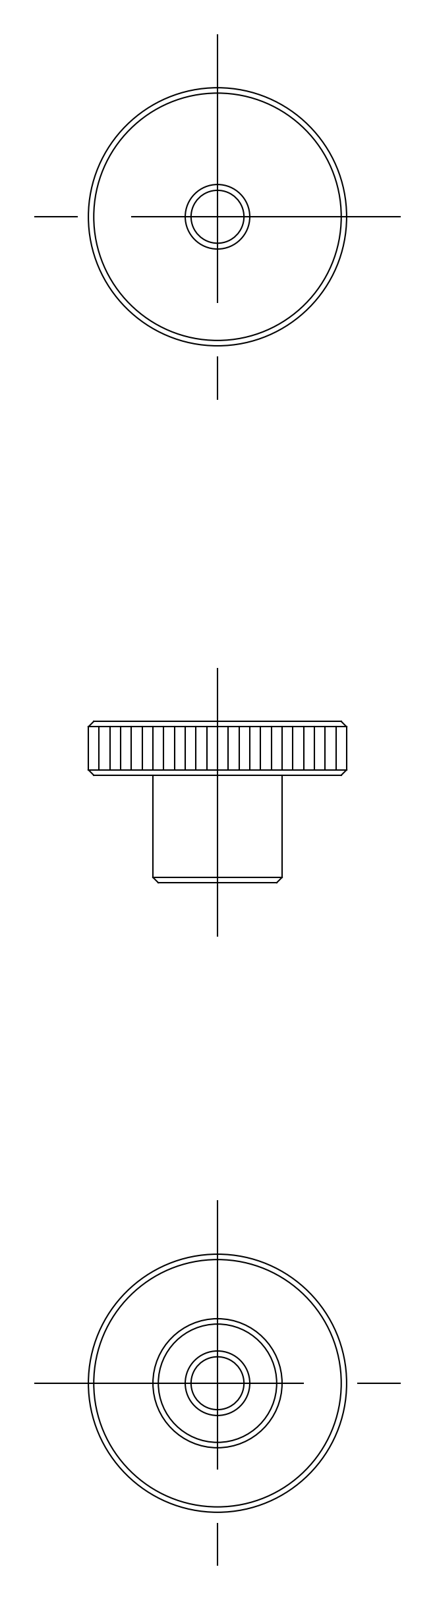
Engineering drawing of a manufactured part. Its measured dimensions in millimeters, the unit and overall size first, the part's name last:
Units: millimetres
Overall size (bounding box): 24 × 24 × 15
Volume: 2 950 mm³ · Surface area: 1 830 mm²
Bodies: 1 solid, 15 faces (0 planar, 0 cylindrical, 15 other)
Part name (STEP PRODUCT): knob
STEP written by: CADfix (AUTOMOTIVE_DESIGN)
